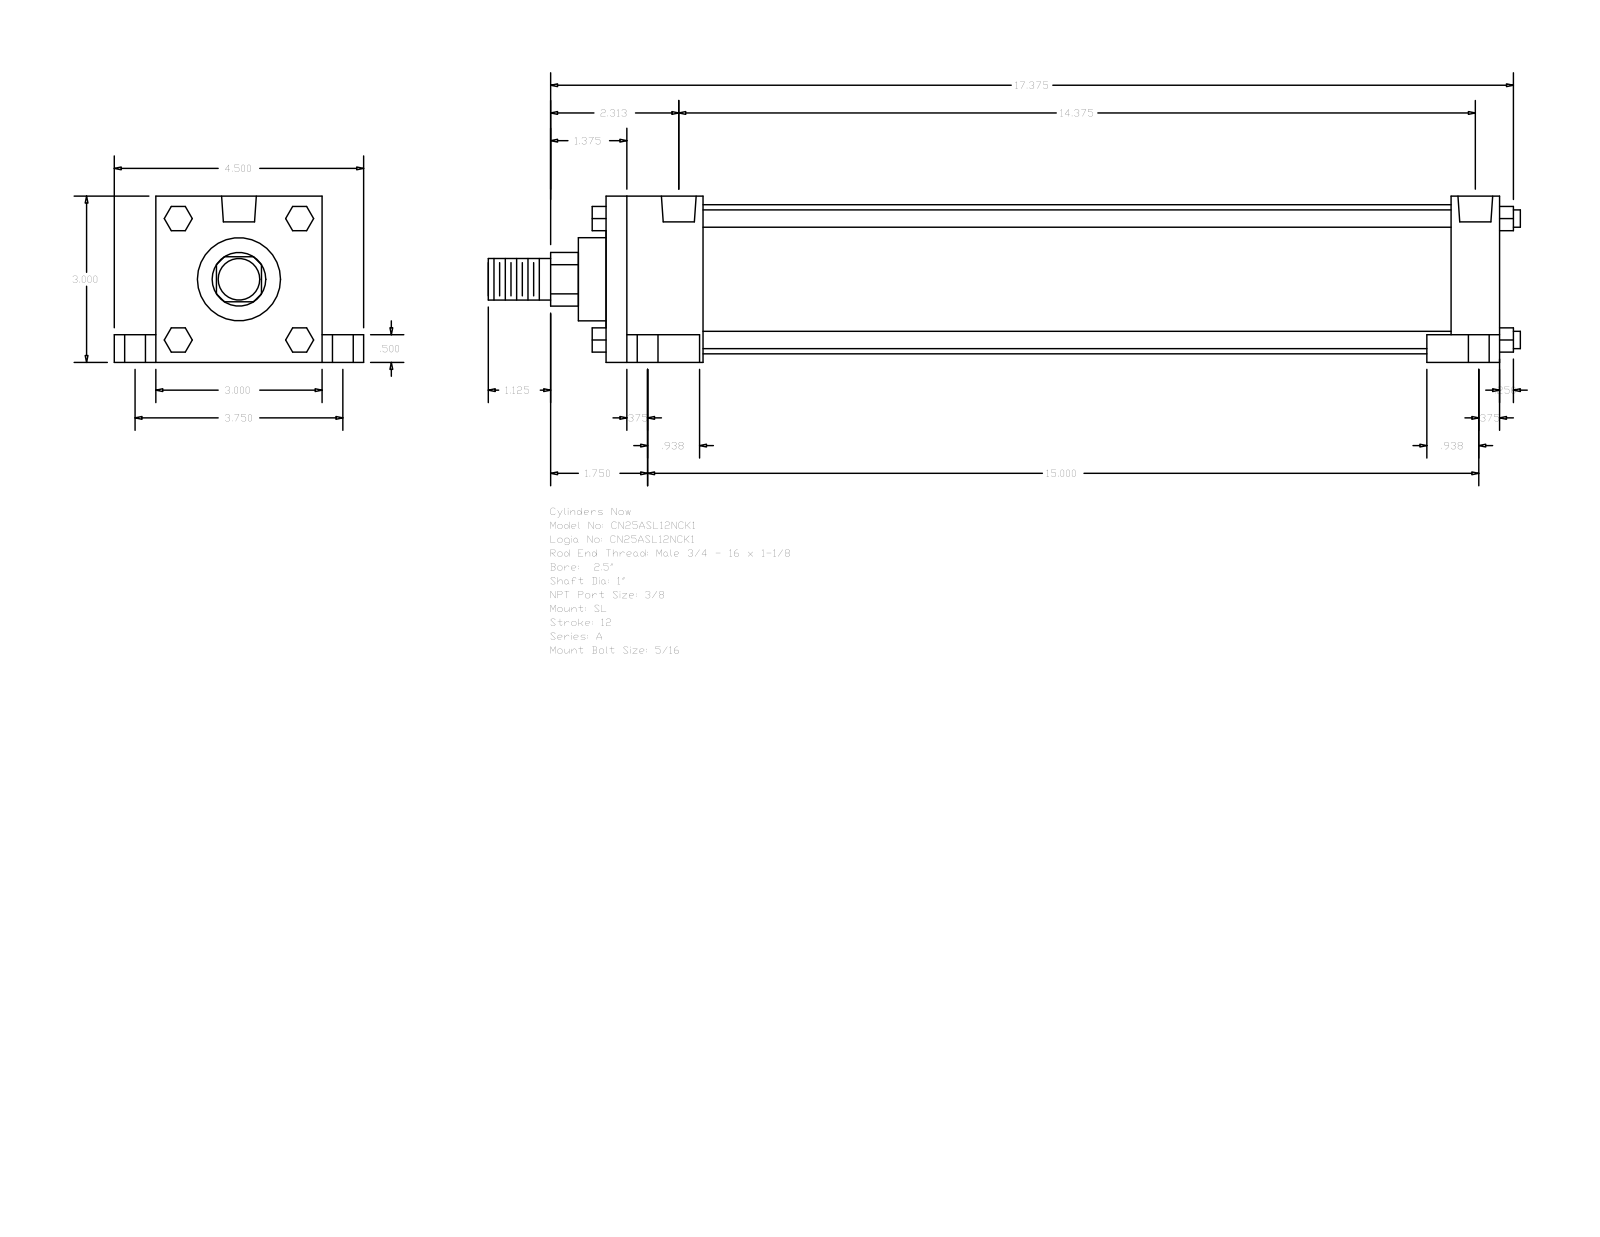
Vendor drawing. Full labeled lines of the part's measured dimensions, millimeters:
Part name (STEP PRODUCT): A_SL__0250_1
STEP written by: GSSL Pune (CONFIG_CONTROL_DESIGN)
Units: millimetres
Bodies: 0 solids, 148 faces (112 planar, 36 cylindrical, 0 other)
Overall size (bounding box): 473.07 × 114.3 × 76.2
Round holes (diameter × count): ⌀5.56 ×4, ⌀9.53 ×4, ⌀15.88 ×4, ⌀15.93 ×2
Round bosses / shafts (diameter × count): ⌀7.94 ×4, ⌀68.33 ×1, ⌀38.1 ×1, ⌀25.4 ×1, ⌀19.05 ×1
Partial cylindrical surfaces — rounded edges, fillets, slot ends (radius × count): R12.29 ×1
Main face-to-face distances: 76.2, 409.58, 12.7, 44.45, 365.13, 387.35, 342.9, 22.23, 19.05, 63.5
Hole centre spacings: 2.38, 47.63, 47.65, 49.09, 49.72, 95.24, 367.5, 369.79
